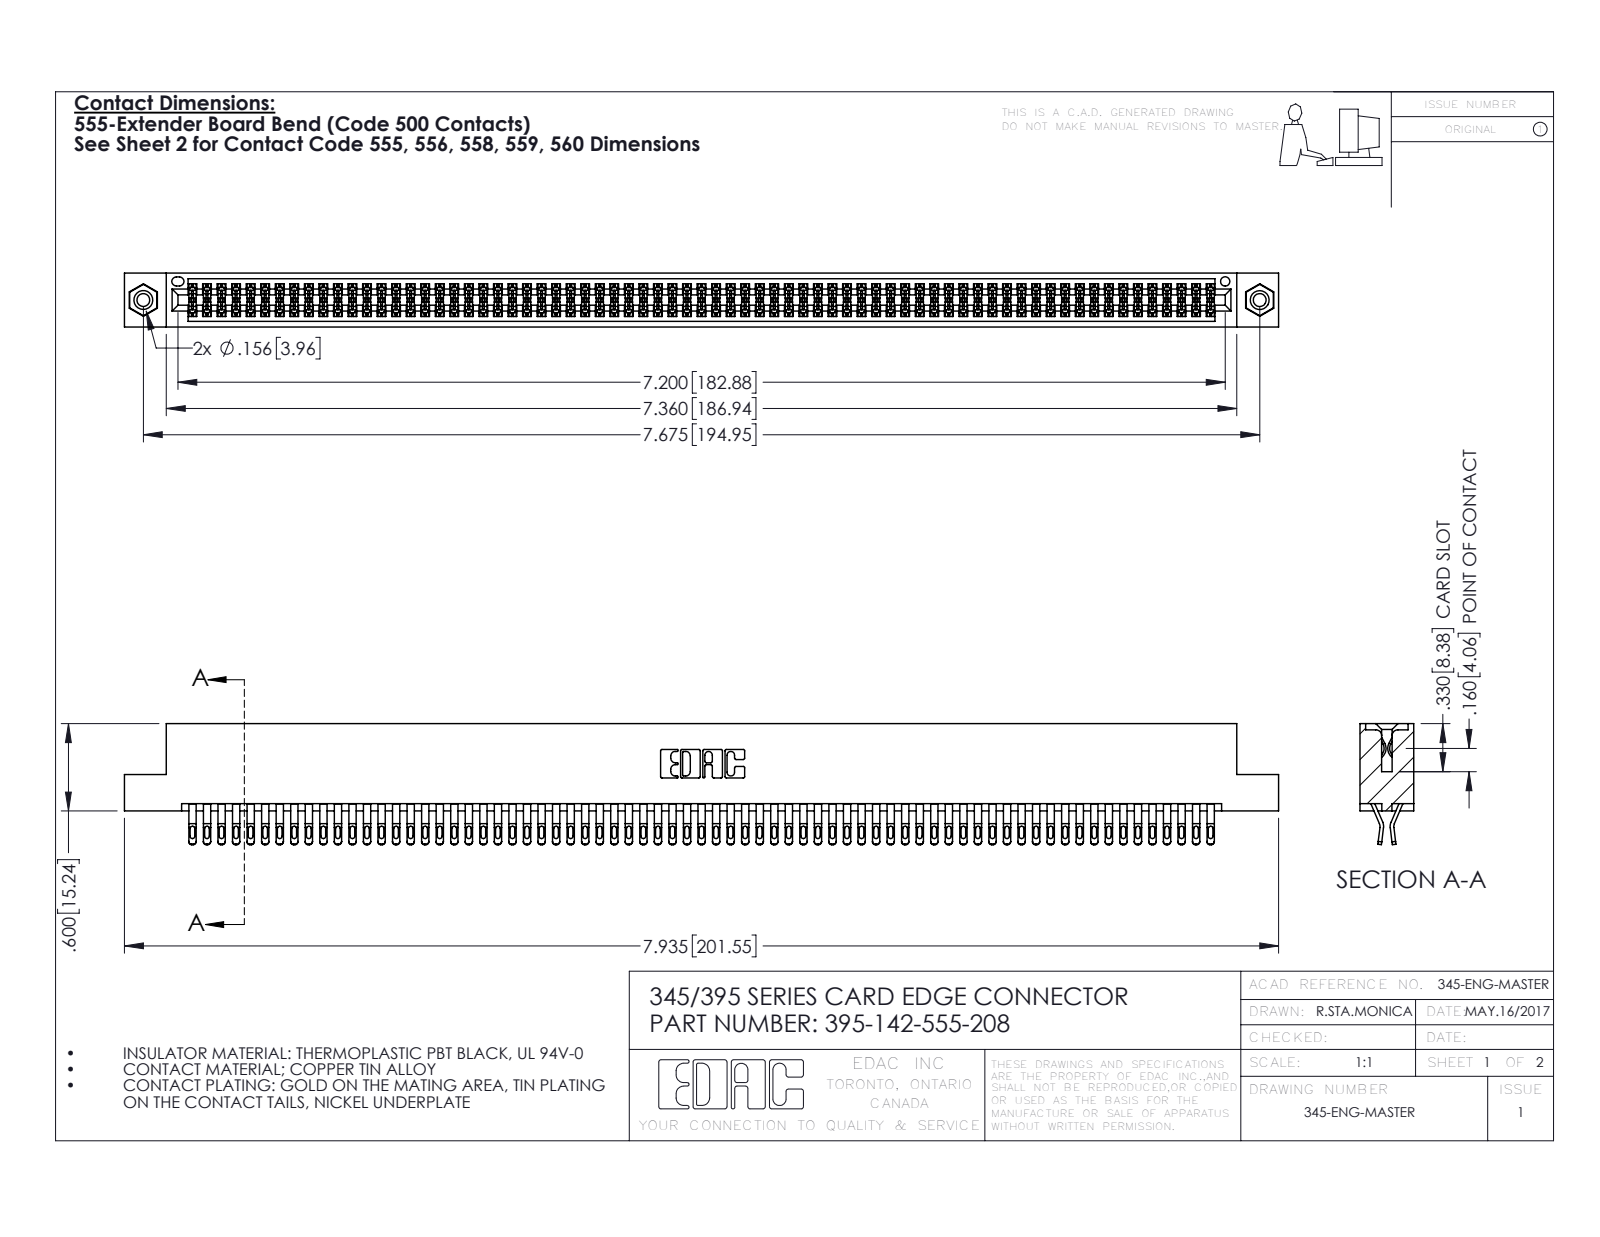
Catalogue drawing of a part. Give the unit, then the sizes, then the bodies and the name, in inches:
Units: inches
Overall size (bounding box): 7.935 × 0.832 × 0.37
Round holes (diameter × count): ⌀0.089 ×2, ⌀0.125 ×2, ⌀0.156 ×2, ⌀0.064 ×1
Round bosses / shafts (diameter × count): ⌀0.155 ×2
Partial cylindrical surfaces — rounded edges, fillets, slot ends (radius × count): R0.016 ×355, R0.02 ×284, R0.006 ×213, R0.01 ×22, R0.007 ×6, R0.031 ×6, R0.026 ×3, R0.01 ×2
Main face-to-face distances: 0.072, 0.298, 0.025, 0.37, 0.2, 0.098, 0.272, 0.225, 0.175, 0.149
Hole centre spacings: 0.27, 7.439, 7.675
Volume: 1.236 in³ · Surface area: 49.52 in²
Bodies: 145 solids, 8138 faces (4514 planar, 3608 cylindrical, 16 other)
Part name (STEP PRODUCT): 395-142-555-208; 345 Part_Flush Mounting Lugs - 0.156 Dia-TI; 345-292-001_555 Tail; 345-250-001_345-250-003-102
STEP written by: SolidWorks 2016 (CONFIG_CONTROL_DESIGN)
